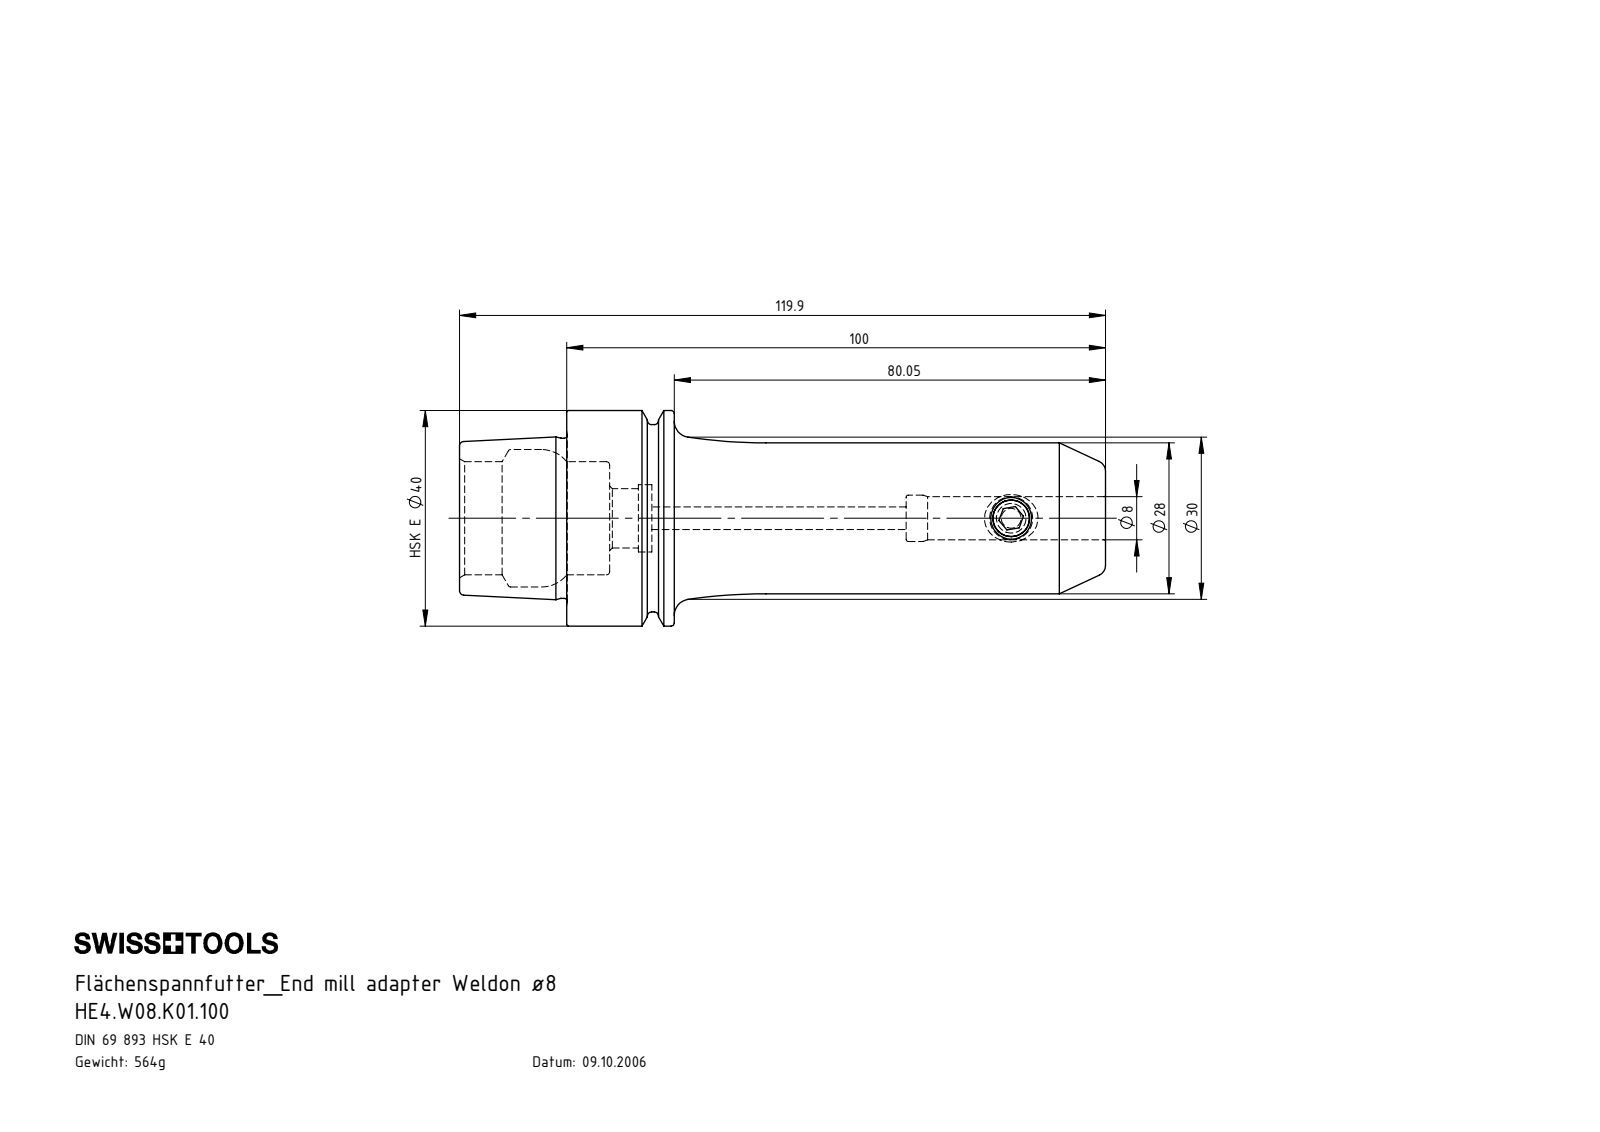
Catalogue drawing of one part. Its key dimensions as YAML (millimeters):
part_name: "HE4.W08.K01.100; W08-ER1.001.010; HE4-W08.K01.100_B_Fertigbearbeitung"
step_written_by: "SolidWorks 2017 (CONFIG_CONTROL_DESIGN)"
units: millimeters
bodies: {solids: 2, faces: 111, planar: 19, cylindrical: 30, other: 62}
overall_size: [119.9, 40, 40]
volume: 71813
surface_area: 18059
round_holes:
  - {diameter: 4.2, count: 1}
  - {diameter: 6.8, count: 1}
  - {diameter: 8, count: 1}
  - {diameter: 8.6, count: 1}
  - {diameter: 11, count: 1}
  - {diameter: 12.5, count: 1}
  - {diameter: 21, count: 1}
  - {diameter: 25.5, count: 1}
round_bosses_or_shafts:
  - {diameter: 40, count: 1}
  - {diameter: 34.75, count: 1}
  - {diameter: 29.71, count: 1}
  - {diameter: 28, count: 1}
  - {diameter: 8, count: 1}
face_to_face_distances: [7.95, 19.9, 27.85, 119.9, 100, 92.05, 39.85, 19.95, 12, 80.05]
